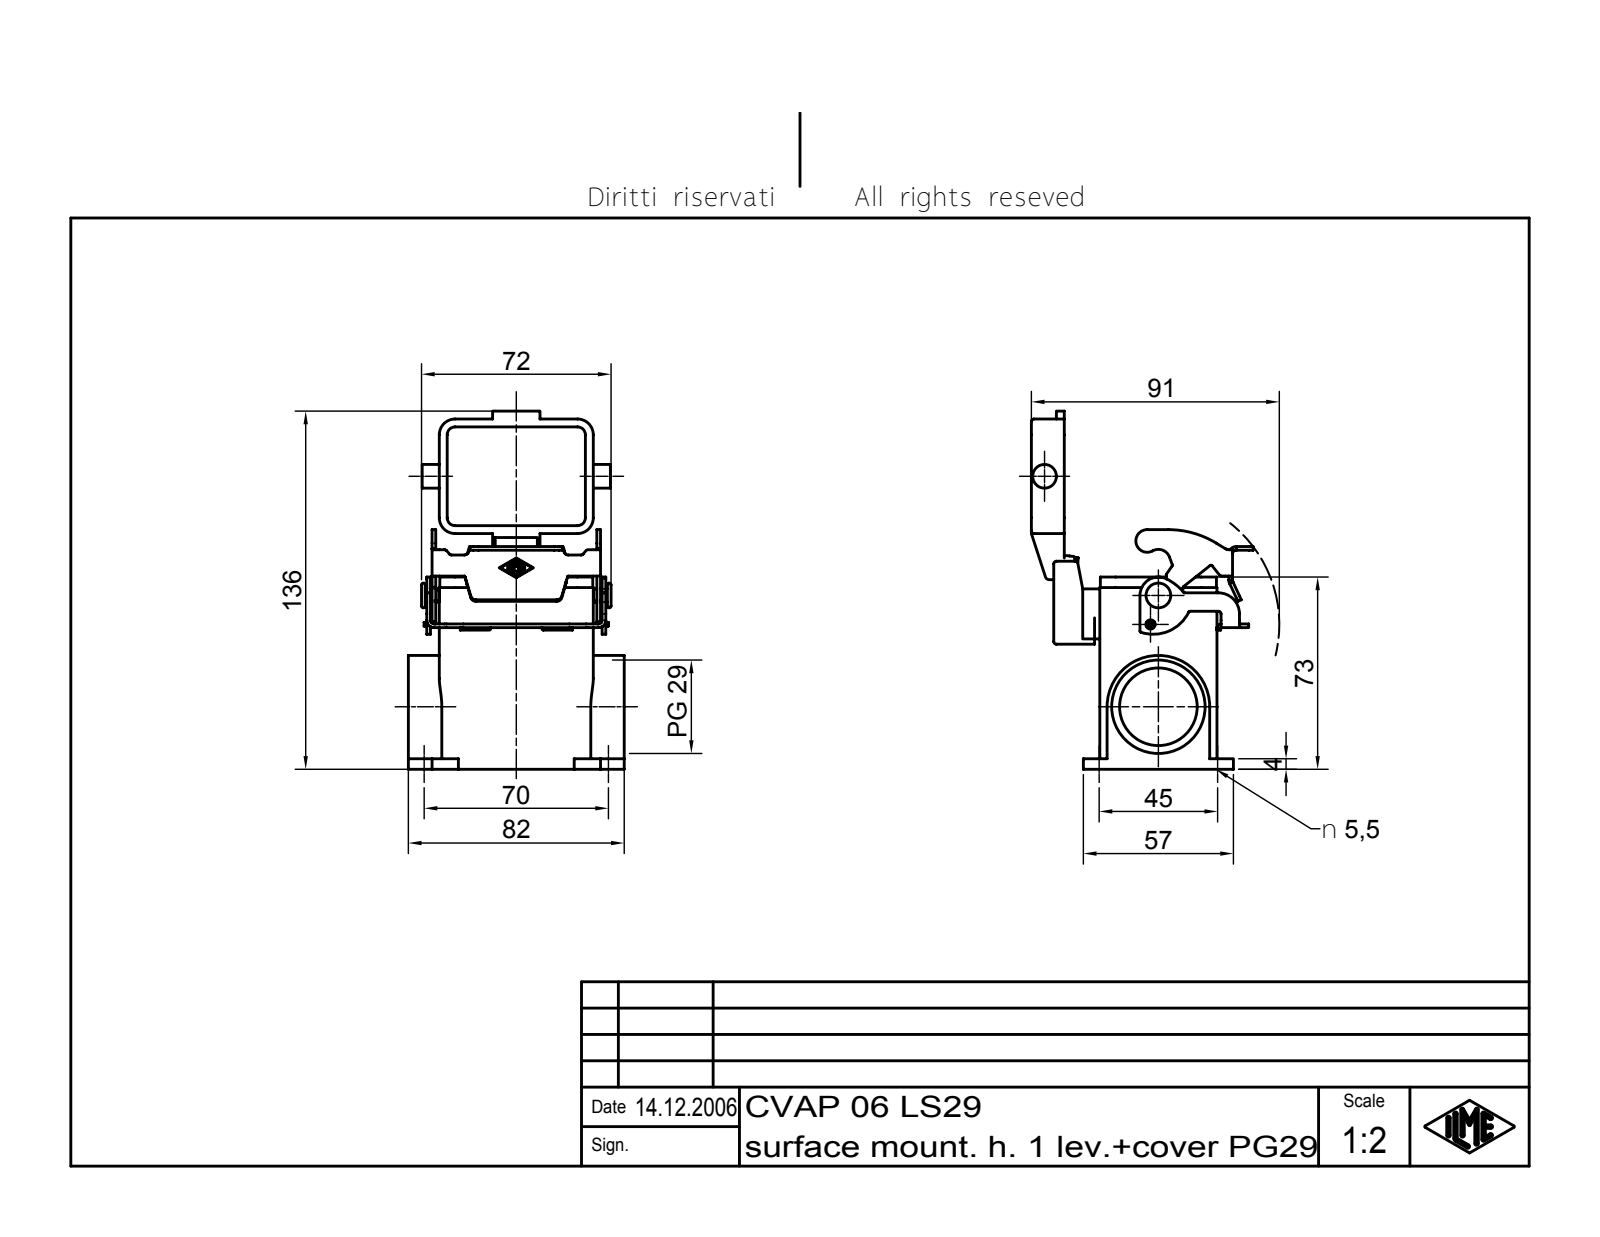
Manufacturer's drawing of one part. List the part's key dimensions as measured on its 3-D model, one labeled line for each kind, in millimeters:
Part name (STEP PRODUCT): CVAP 06 LS29
STEP written by: Autodesk Inventor 7 (AUTOMOTIVE_DESIGN)
Units: millimetres
Bodies: 4 solids, 572 faces (222 planar, 185 cylindrical, 165 other)
Overall size (bounding box): 136 × 84.23 × 82
Volume: 113 063 mm³ · Surface area: 63 741 mm²
Round holes (diameter × count): ⌀5.5 ×4, ⌀3.5 ×1, ⌀4 ×1, ⌀29.48 ×1, ⌀35.48 ×1
Round bosses / shafts (diameter × count): ⌀5 ×2, ⌀9 ×1, ⌀7 ×1, ⌀3.2 ×1, ⌀3 ×1
Partial cylindrical surfaces — rounded edges, fillets, slot ends (radius × count): R1 ×27, R0.25 ×15, R0.5 ×10, R1.5 ×10, R6 ×8, R2 ×7, R1.4 ×6, R2.8 ×6
Main face-to-face distances: 4, 40.5, 44.5, 26, 2.5, 30, 36.5, 70.5, 66.5, 68
Hole centre spacings: 45, 70, 83.22, 31.4
